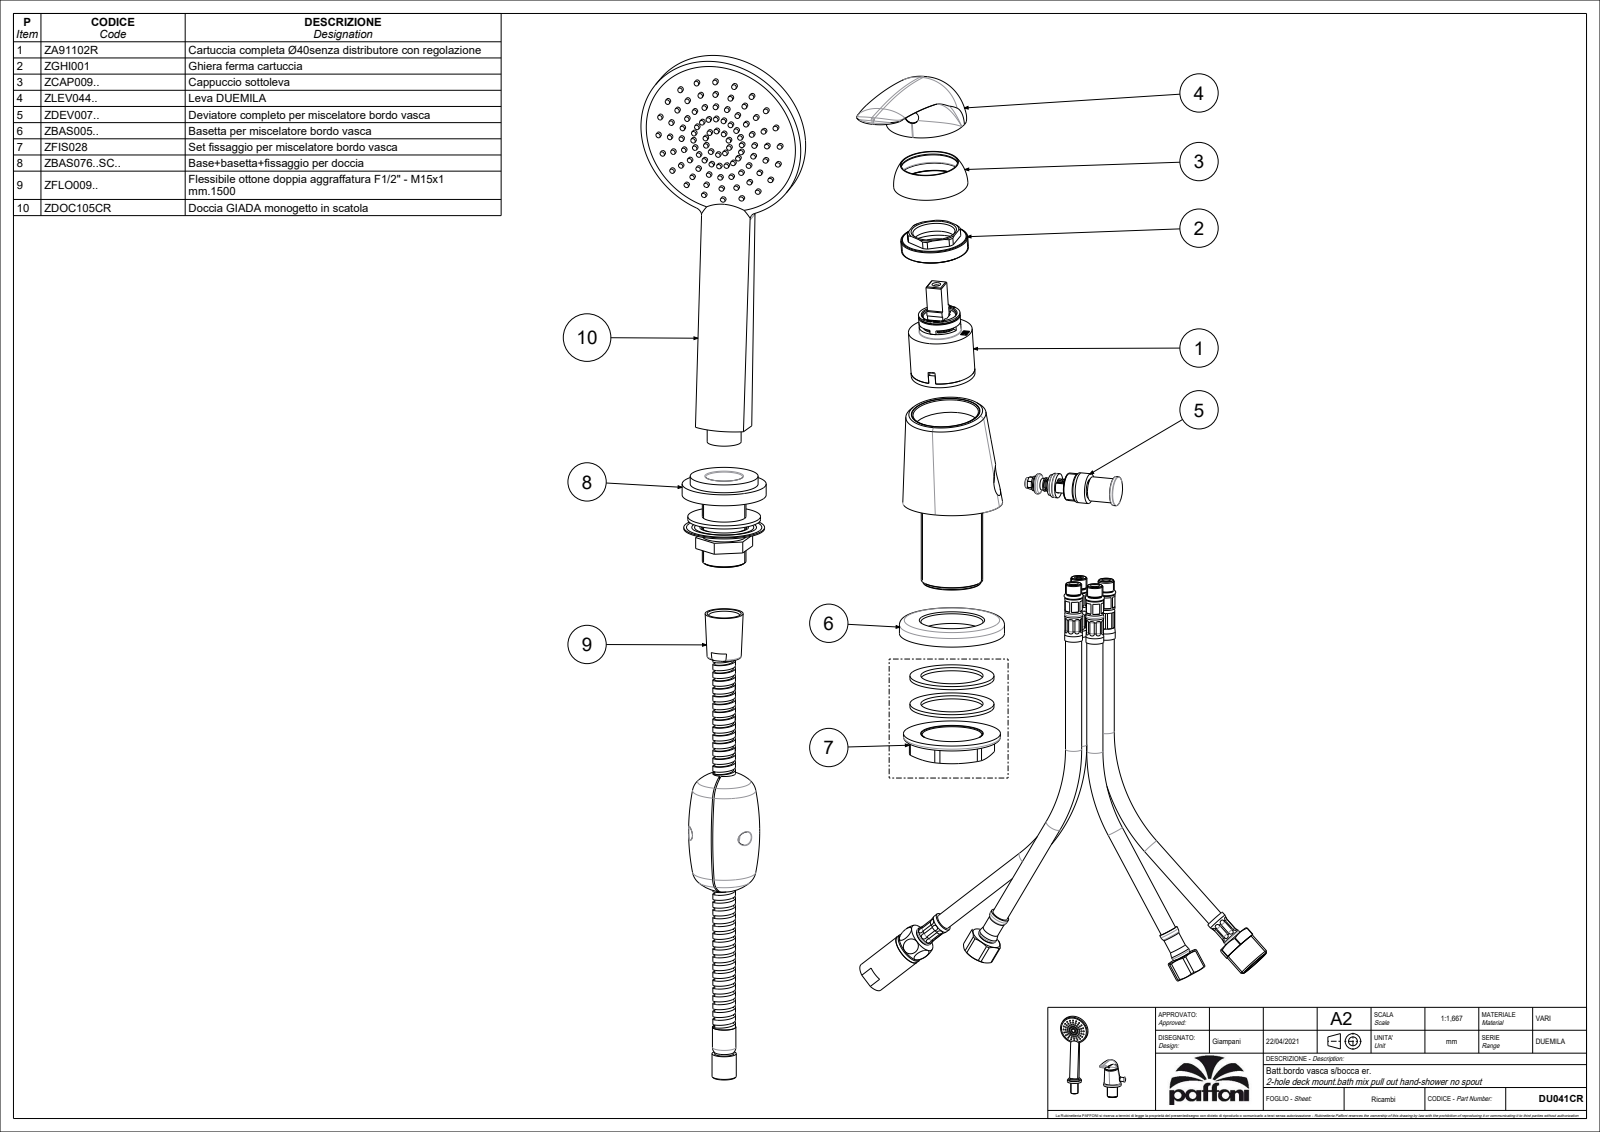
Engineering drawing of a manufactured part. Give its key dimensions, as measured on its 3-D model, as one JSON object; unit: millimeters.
{"part_name": "DU041CR", "step_written_by": "CREO PARAMETRIC BY PTC INC, 2020044 (CONFIG_CONTROL_DESIGN)", "units": "millimeters", "bodies": {"solids": 2, "faces": 407, "planar": 31, "cylindrical": 221, "other": 155}, "overall_size": [252.7, 251.5, 142.23], "volume_mm3": 473013, "surface_area_mm2": 75504, "round_holes": [[9.2, 1], [15.8, 1], [18.2, 1], [19, 1]], "round_bosses_or_shafts": [[3, 90], [105, 1], [65, 1], [52, 1], [42, 1], [18.5, 1], [18.1, 1], [18, 1]], "partial_cylinders_radius": [[1.5, 2], [15, 2], [24, 2], [24.5, 2], [18, 1], [39.04, 1], [340.59, 1], [341.58, 1]], "face_to_face_distances": [7, 12, 5, 3.5, 8.5, 1.5, 14, 5.5, 2, 11.01]}
